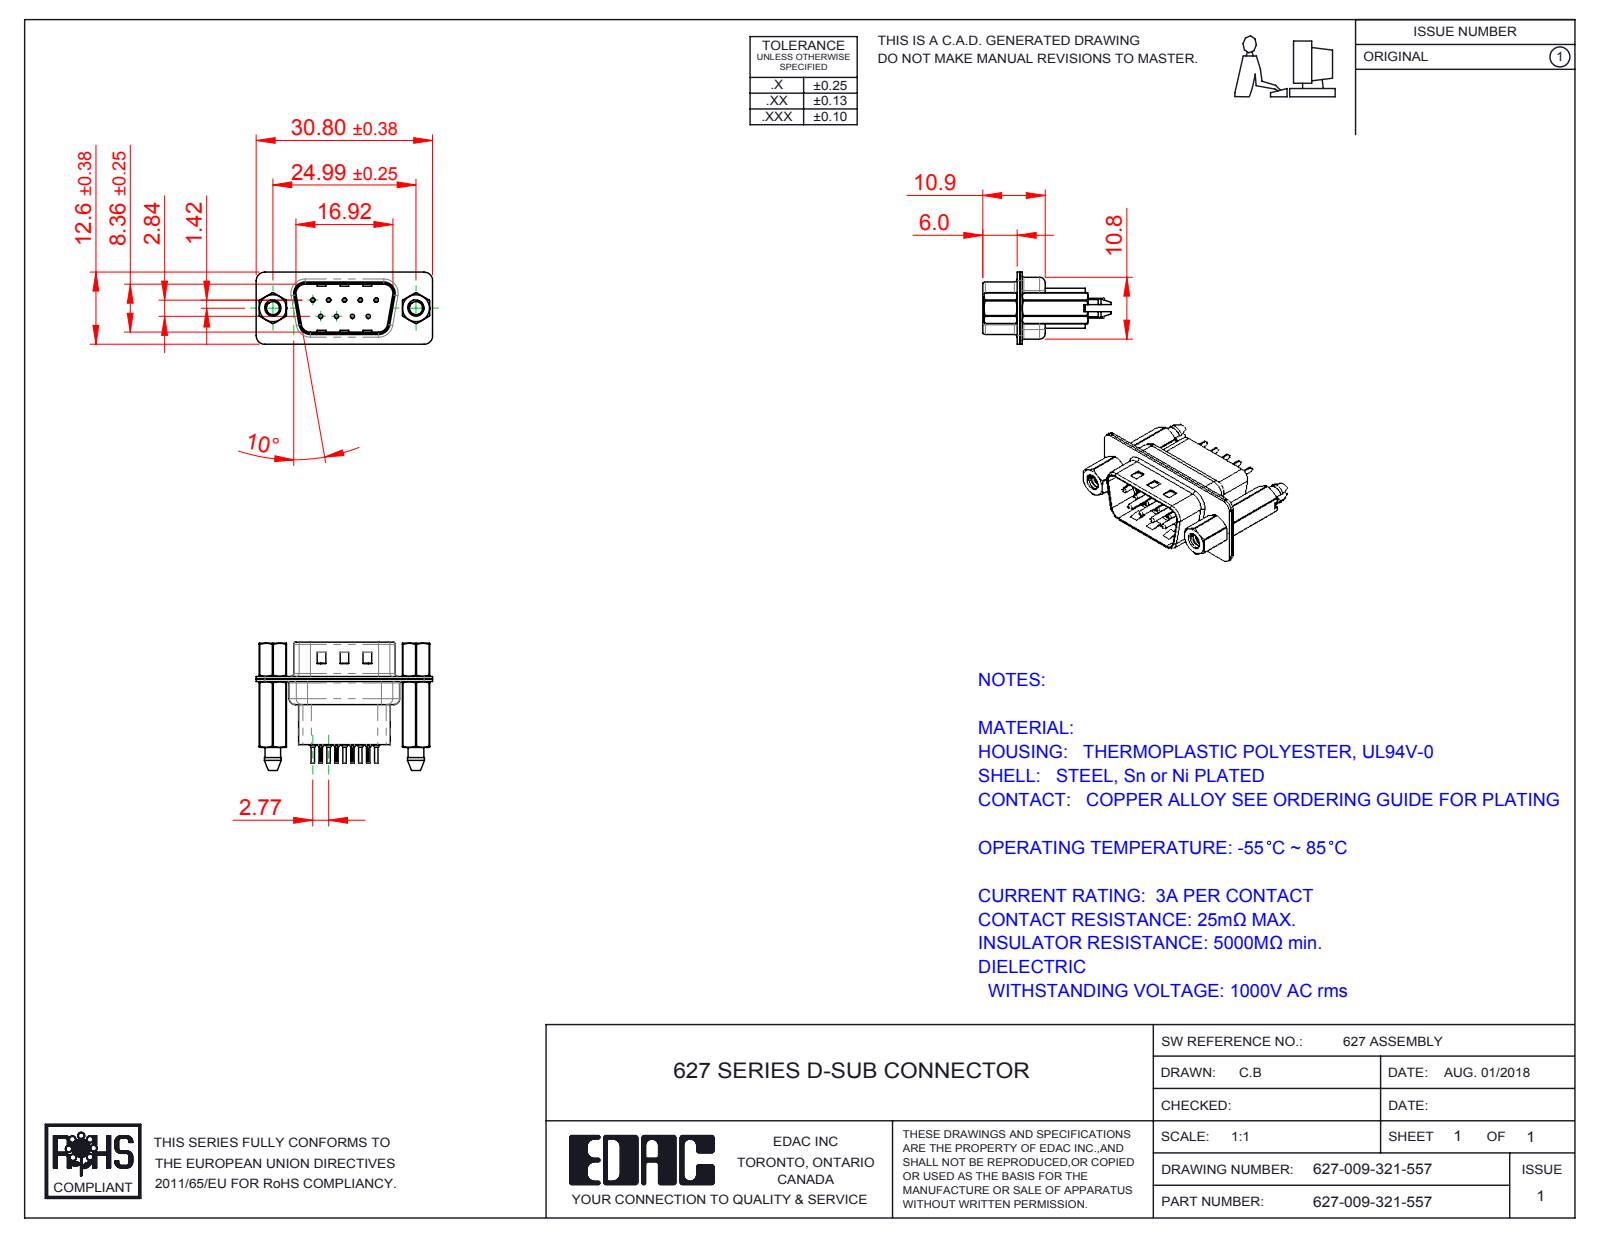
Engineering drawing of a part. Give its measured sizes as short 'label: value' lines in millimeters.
name: 627 4-40 Hex Standoff; 627-009-321-557; 627 Contact Row 1_21H; 627 4-40 Threaded Boardlock_HP (+4 more)
written by: SolidWorks 2016 (CONFIG_CONTROL_DESIGN)
unit: mm
bodies: 16 solids, 1420 faces (377 planar, 600 cylindrical, 443 other)
size: 30.8 × 22.4 × 12.6
volume: 2 304 mm³; area: 5 874 mm²
holes: 9× ⌀0.2, 9× ⌀0.35, 9× ⌀1.1, 9× ⌀1.6, 2× ⌀2.26, 2× ⌀2.29, 2× ⌀4, 2× ⌀4.8
bosses: 9× ⌀2, 9× ⌀1.5, 9× ⌀0.75, 9× ⌀0.6, 2× ⌀4.9, 2× ⌀2.79
rounds: 20× R1.5, 18× R0.1, 12× R2, 10× R1.6, 8× R0.5, 4× R0.25, 4× R0.6, 4× R0.65
face distances: 0.45, 0.4, 0.9, 4.76, 0.82, 9.58, 1.4, 1.5, 0.68, 7.68
hole spacings: 3.16, 2.77, 5.54, 5.03, 5.04, 8.31, 7.48, 7.49
